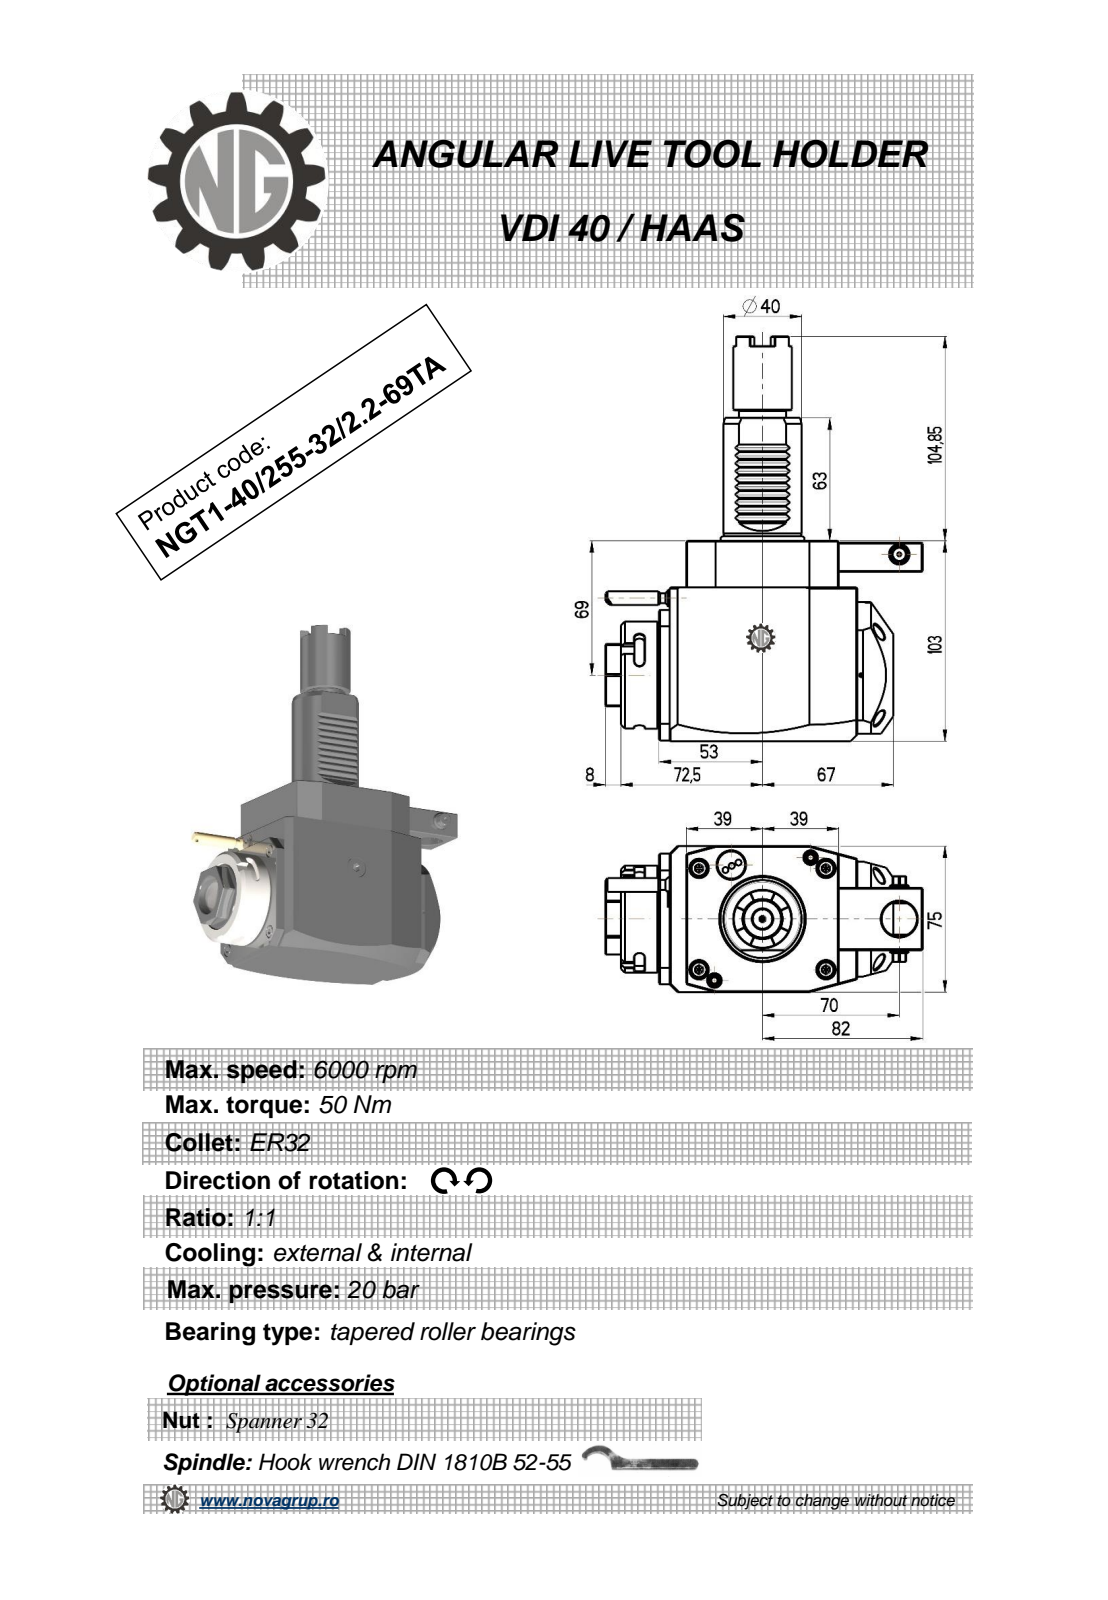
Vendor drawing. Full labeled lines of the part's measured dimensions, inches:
Part name (STEP PRODUCT): NGT1_40_255_32_1_2_69TA
STEP written by: PRO/ENGINEER BY PARAMETRIC TECHNOLOGY CORPORATION, 2010280 (CONFIG_CONTROL_DESIGN)
Units: inches
Bodies: 1 solid, 393 faces (219 planar, 86 cylindrical, 88 other)
Overall size (bounding box): 8.183 × 6.398 × 2.953
Volume: 56.9 in³ · Surface area: 115.2 in²
Round holes (diameter × count): ⌀0.079 ×1, ⌀0.098 ×1, ⌀0.118 ×1, ⌀0.374 ×1, ⌀0.709 ×1, ⌀0.787 ×1, ⌀0.906 ×1
Round bosses / shafts (diameter × count): ⌀0.353 ×2, ⌀2.165 ×1, ⌀1.89 ×1, ⌀1.575 ×1, ⌀1.181 ×1, ⌀0.945 ×1, ⌀0.394 ×1, ⌀0.276 ×1
Partial cylindrical surfaces — rounded edges, fillets, slot ends (radius × count): R0.012 ×10, R0.098 ×6, R7.087 ×2, R0.02 ×1, R0.152 ×1, R0.167 ×1, R0.965 ×1, R1.476 ×1
Main face-to-face distances: 2.953, 4.055, 1.319, 0.768, 3.11, 0.315, 0.551, 4.016, 0.846, 3.425
Hole centre spacings: 1.107, 1.701, 2.421, 2.756
